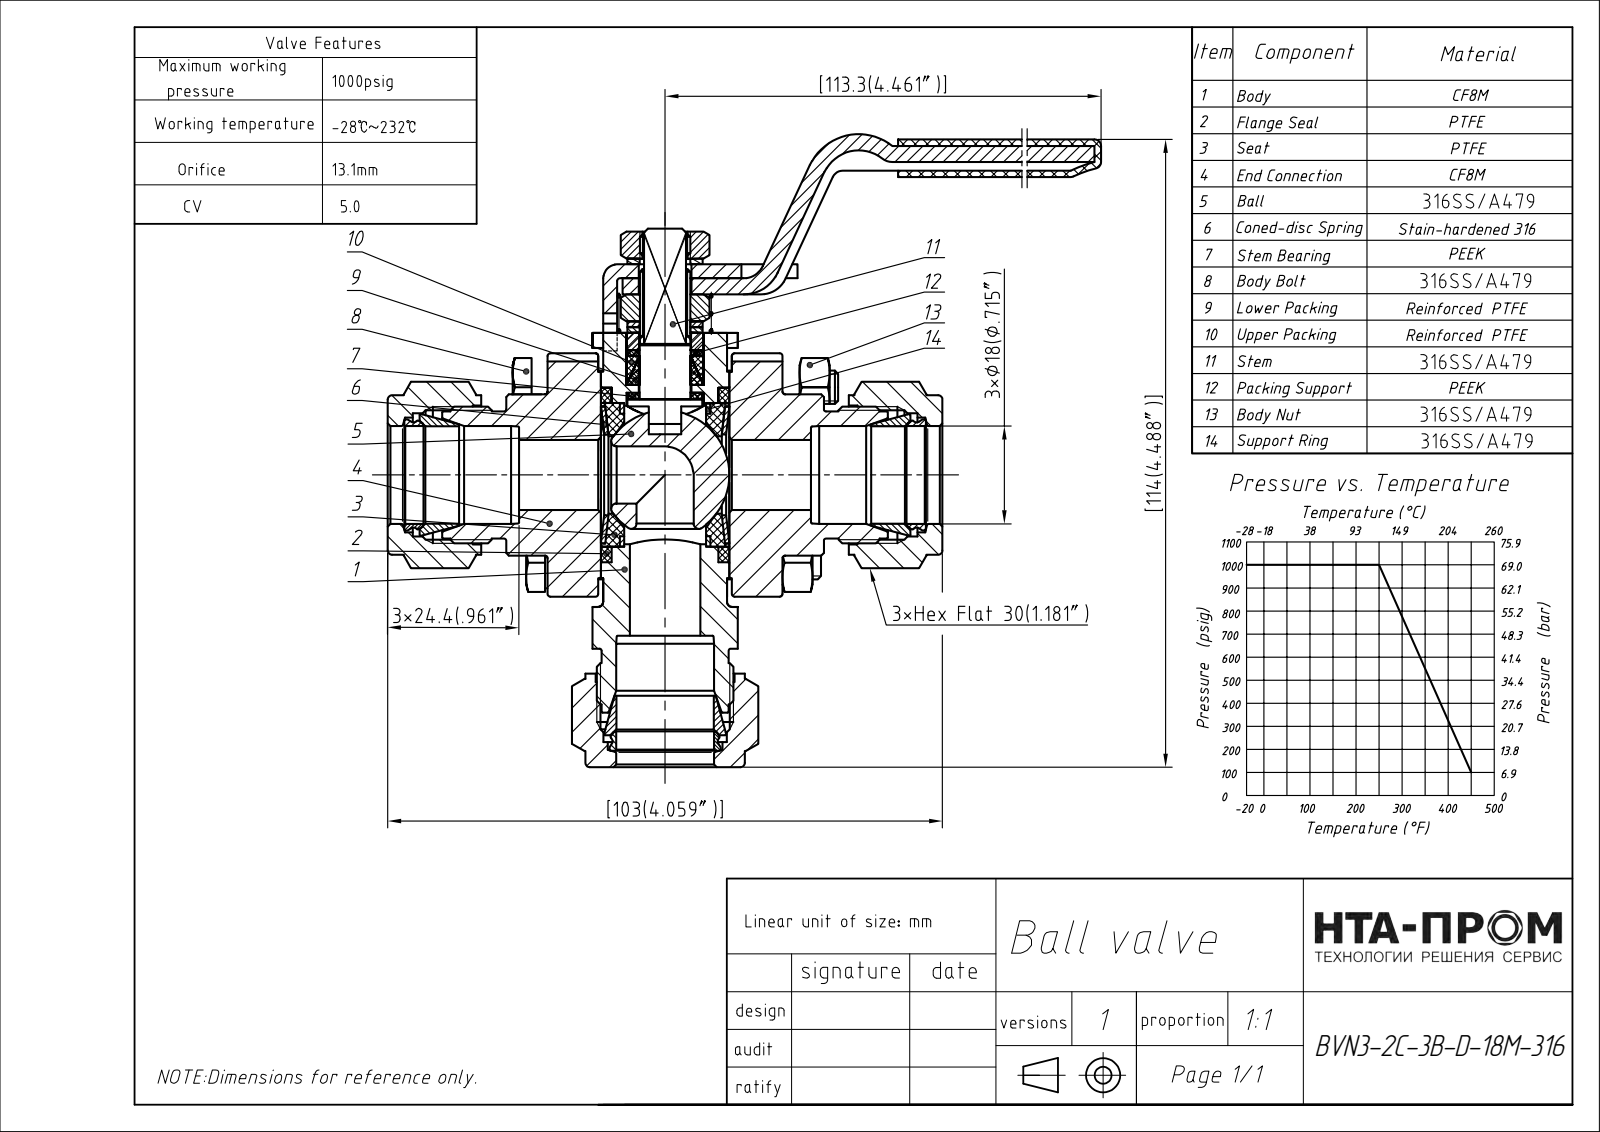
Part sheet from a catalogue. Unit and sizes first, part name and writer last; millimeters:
Units: millimetres
Overall size (bounding box): 164.35 × 113.56 × 45.38
Round holes (diameter × count): ⌀4.98 ×4, ⌀6.8 ×4, ⌀6.7 ×1, ⌀9 ×1, ⌀9.36 ×1, ⌀13.1 ×1, ⌀18 ×1, ⌀18.13 ×1, ⌀18.15 ×1, ⌀18.18 ×1, ⌀20 ×1, ⌀21.35 ×1
Round bosses / shafts (diameter × count): ⌀6 ×4, ⌀29.6 ×2, ⌀25.4 ×2, ⌀23.63 ×2, ⌀30 ×1, ⌀23.5 ×1, ⌀22.64 ×1, ⌀20.67 ×1
Partial cylindrical surfaces — rounded edges, fillets, slot ends (radius × count): R0.5 ×20, R1 ×14, R6 ×6, R6.5 ×4, R1.2 ×3, R4 ×3, R1.5 ×2, R2 ×2
Main face-to-face distances: 30, 42.64, 85.02, 7, 5.5, 78.02, 18.8, 61.72, 9.82, 32.82
Hole centre spacings: 22.9, 32.38, 45.79, 1.3
Volume: 130 713 mm³ · Surface area: 59 017 mm²
Bodies: 17 solids, 928 faces (243 planar, 340 cylindrical, 345 other)
Part name (STEP PRODUCT): BVN3-2C-3B-D-18M-316
STEP written by: FreeCAD (AUTOMOTIVE_DESIGN)
